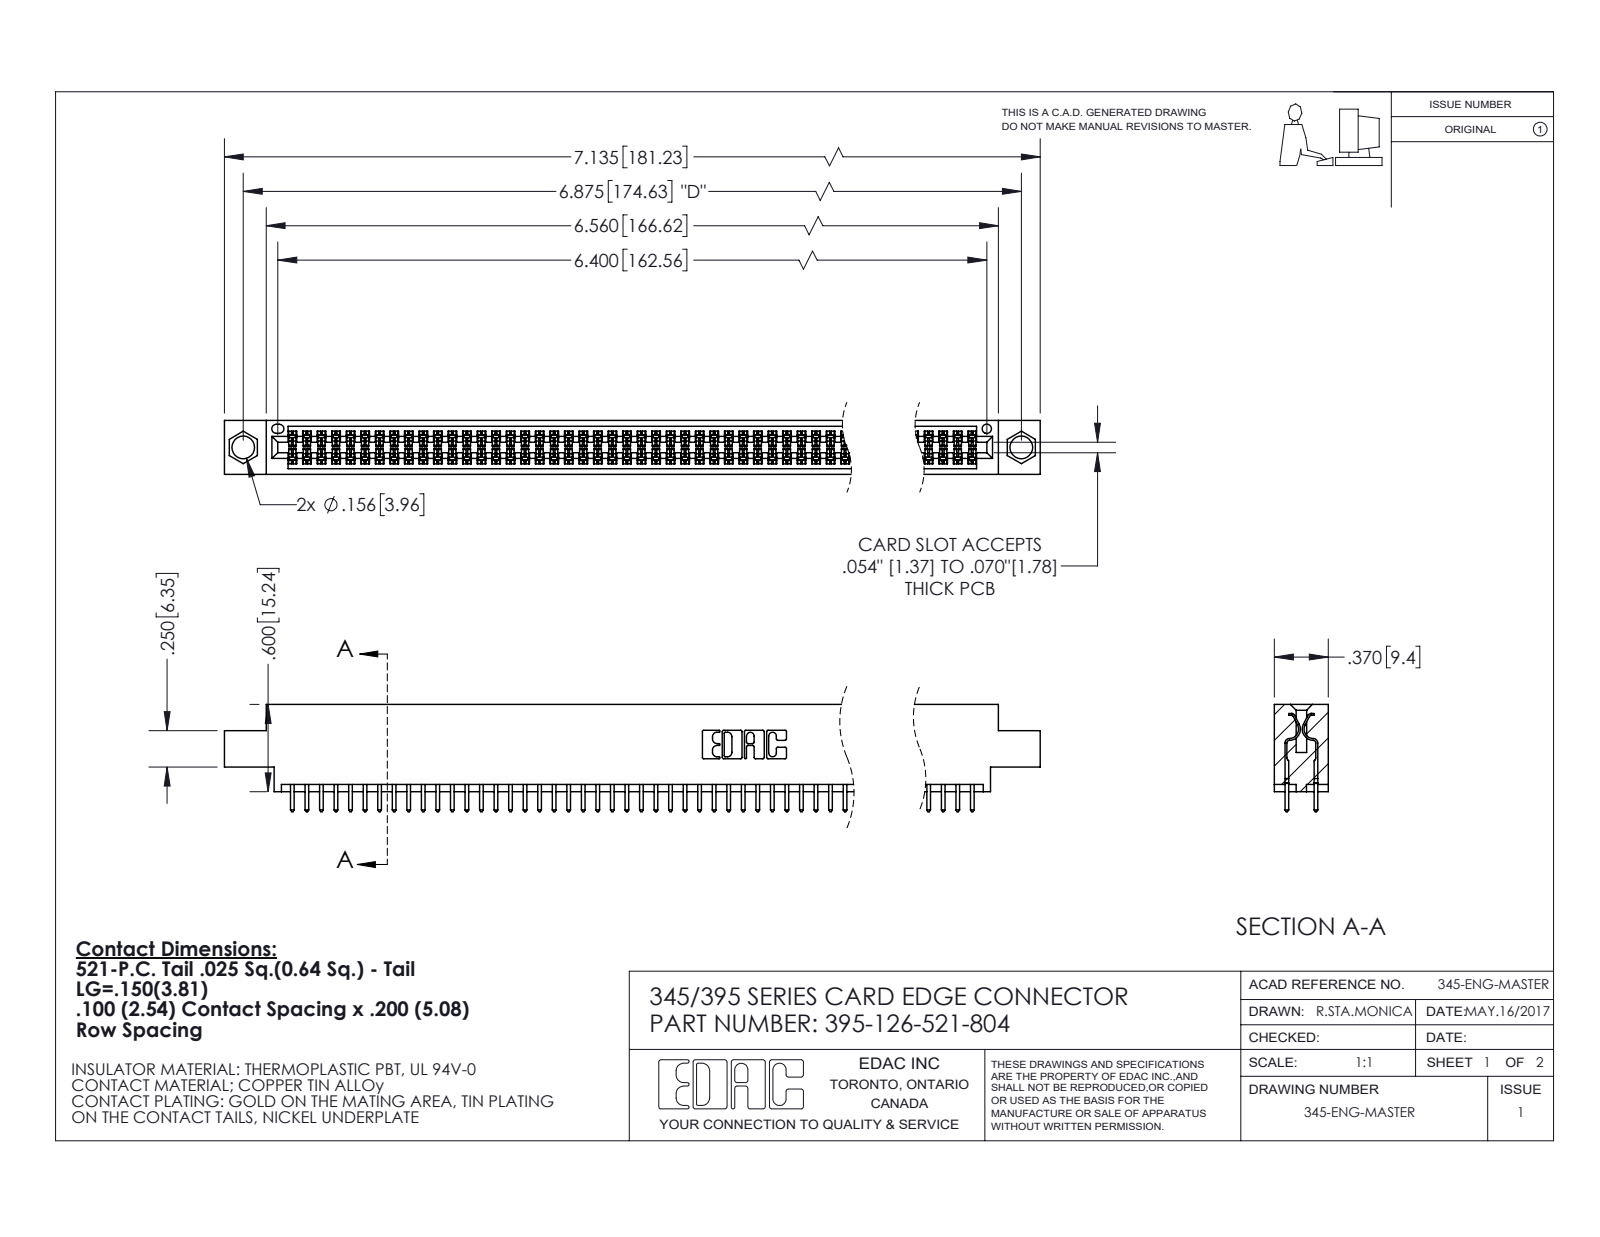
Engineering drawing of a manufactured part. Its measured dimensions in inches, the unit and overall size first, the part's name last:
Units: inches
Overall size (bounding box): 7.135 × 0.737 × 0.37
Round holes (diameter × count): ⌀0.156 ×2, ⌀0.064 ×1
Partial cylindrical surfaces — rounded edges, fillets, slot ends (radius × count): R0.006 ×190, R0.01 ×126, R0.01 ×22, R0.007 ×6, R0.031 ×6, R0.026 ×3, R0.014 ×2, R0.019 ×2
Main face-to-face distances: 0.072, 0.298, 0.2, 0.37, 0.098, 0.272, 0.025, 0.225, 0.175, 0.149
Hole centre spacings: 0.27, 6.639, 6.875
Volume: 1.07 in³ · Surface area: 40.27 in²
Bodies: 127 solids, 6444 faces (4256 planar, 2188 cylindrical, 0 other)
Part name (STEP PRODUCT): 345-292-001_345-293-121; 395-126-521-804; 345 Part_0.170 Offset - 0.156 Dia-TI
STEP written by: SolidWorks 2020 (CONFIG_CONTROL_DESIGN)
